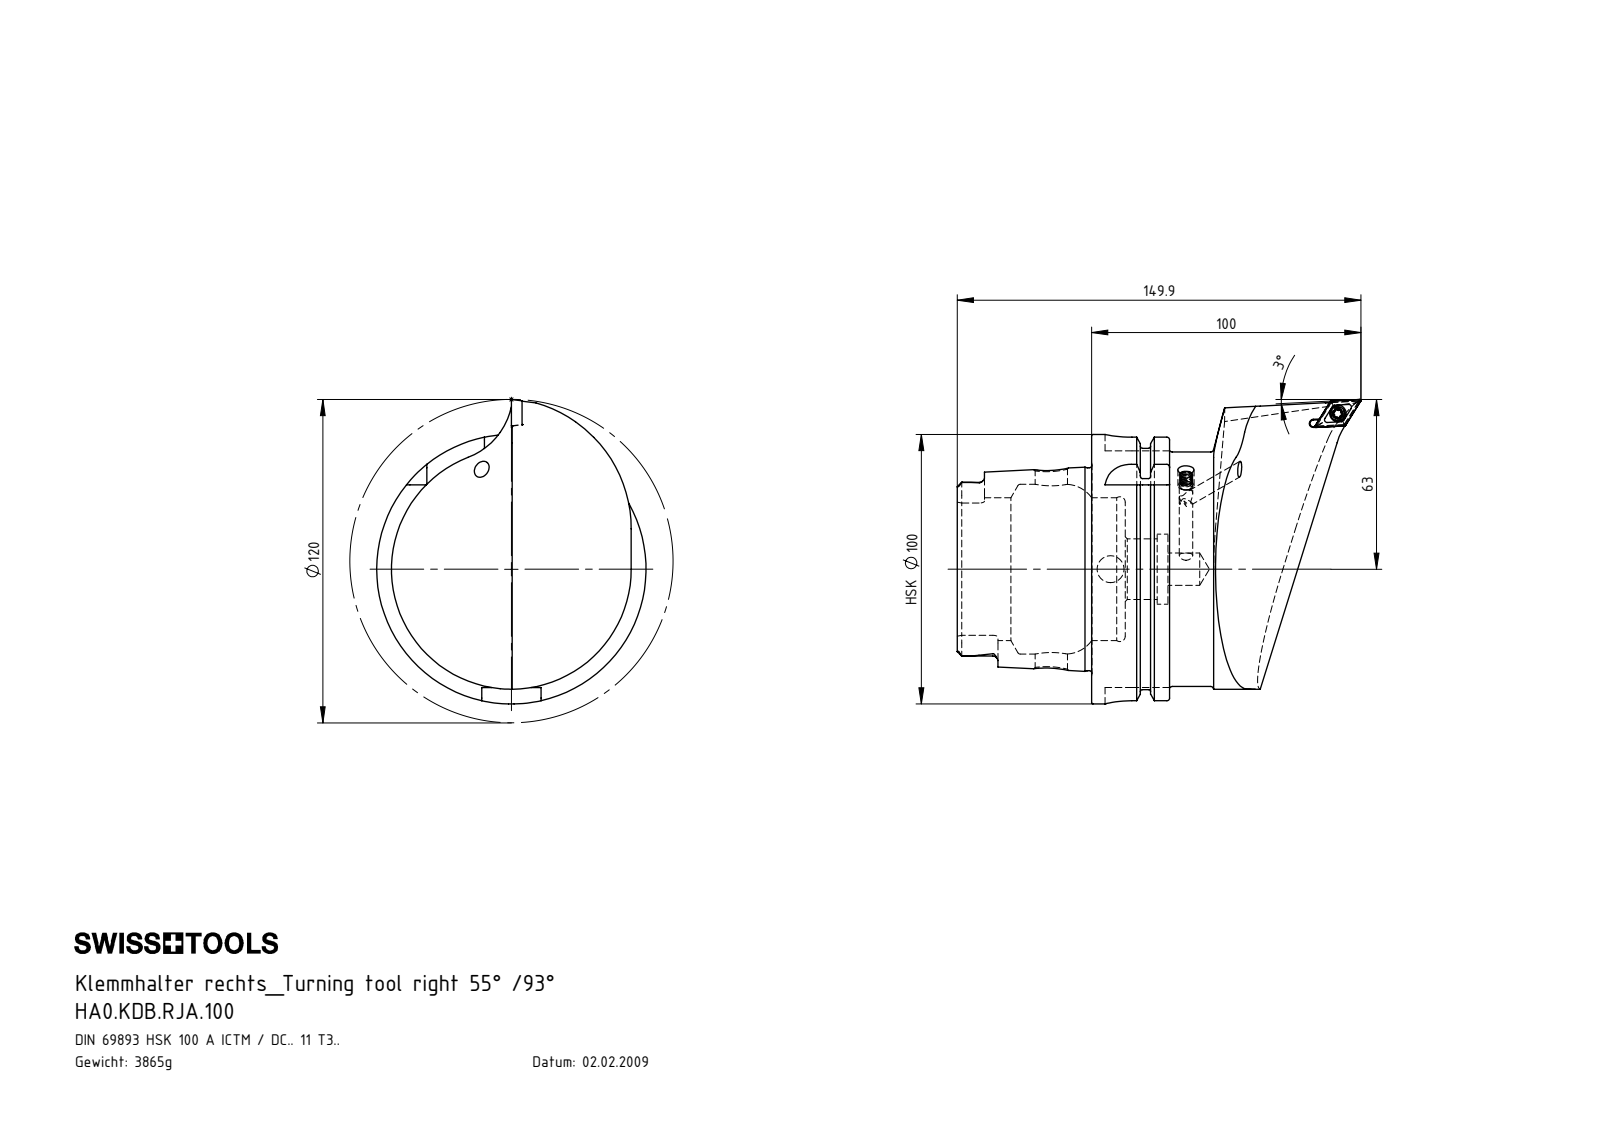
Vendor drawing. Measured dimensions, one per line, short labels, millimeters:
name: HA0.KDB.RJA.100; KVT_MB_600_050; WCB-ER2.001.009_A; DCMT11T304 (+1 more)
written by: SolidWorks 2012 (CONFIG_CONTROL_DESIGN)
unit: mm
bodies: 5 solids, 311 faces (73 planar, 93 cylindrical, 145 other)
size: 149.91 × 113 × 100
volume: 492 045 mm³; area: 66 082 mm²
holes: 2× ⌀12, 1× ⌀3.3, 1× ⌀4, 1× ⌀4.4, 1× ⌀5, 1× ⌀6, 1× ⌀6.1, 1× ⌀10, 1× ⌀22.5, 1× ⌀26, 1× ⌀53, 1× ⌀63
bosses: 1× ⌀100, 1× ⌀91.95, 1× ⌀87, 1× ⌀75.26, 1× ⌀5.25, 1× ⌀5, 1× ⌀4
rounds: 6× R0.34, 6× R0.59, 6× R1.9, 4× R10, 2× R4.83, 2× R4.88, 1× R1.25, 1× R6
face distances: 12.45, 28.95, 16.5, 49.9, 62.35, 78.85, 87.8, 78.2, 28.3, 15.85
hole spacings: 102.22, 102.34
